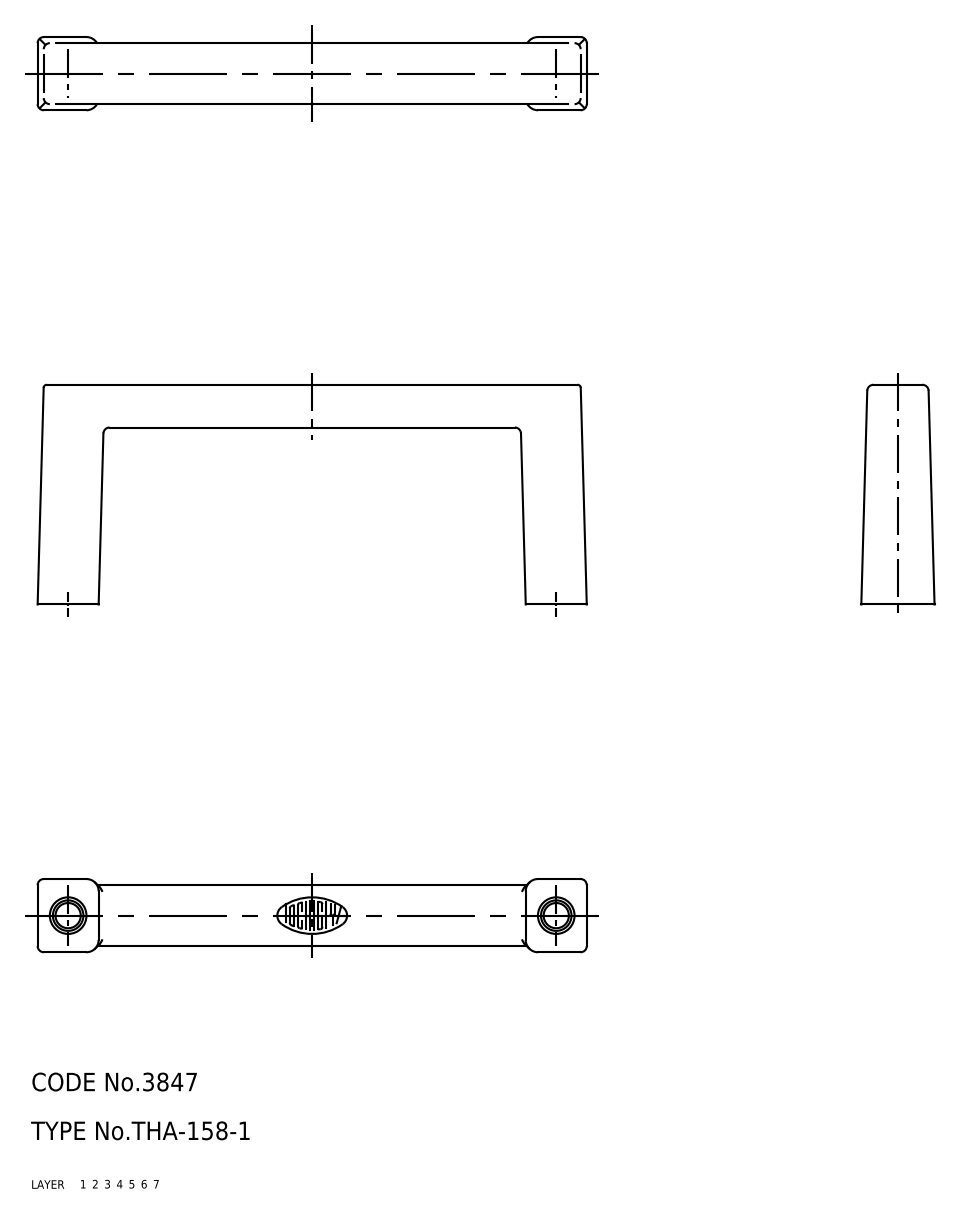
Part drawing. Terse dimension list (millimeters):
name: 67111256
written by: CADfix (AUTOMOTIVE_DESIGN)
unit: mm
bodies: 1 solid, 48 faces (0 planar, 0 cylindrical, 48 other)
size: 90 × 36 × 12
volume: 12 016 mm³; area: 5 662 mm²
